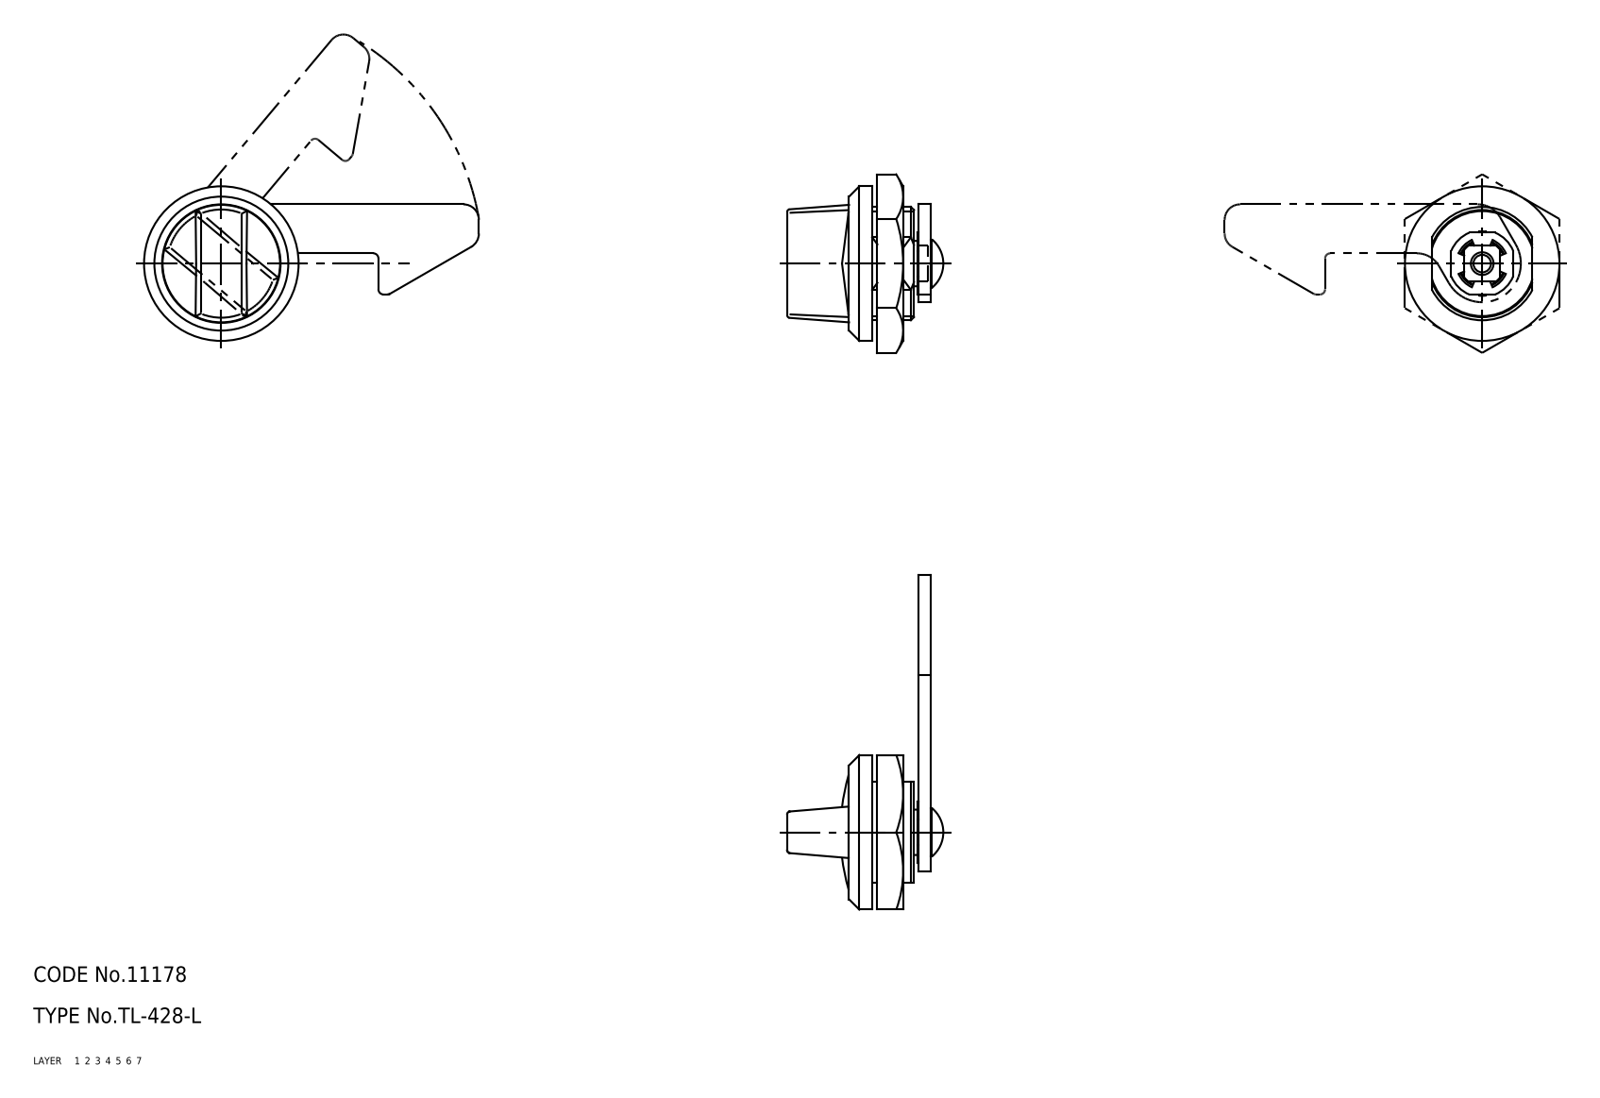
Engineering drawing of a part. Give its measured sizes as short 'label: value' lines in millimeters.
name: 取付ナット; TL-428-L開示用; TL_428_L
written by: SolidWorks 2015 (AUTOMOTIVE_DESIGN)
unit: mm
bodies: 2 solids, 202 faces (66 planar, 66 cylindrical, 70 other)
size: 67.32 × 30.3 × 30
volume: 11 997 mm³; area: 7 239 mm²
holes: 1× ⌀20.38, 1× ⌀23
bosses: 1× ⌀30, 1× ⌀22.8, 1× ⌀20.38, 1× ⌀9.4, 1× ⌀4
rounds: 3× R1, 3× R5, 2× R0.5, 2× R3, 1× R4.4, 1× R4.55, 1× R6.5, 1× R7.5
face distances: 2.3, 9, 11.3, 1.1, 7.9, 10.2, 6.1, 5, 2.9, 5.2
